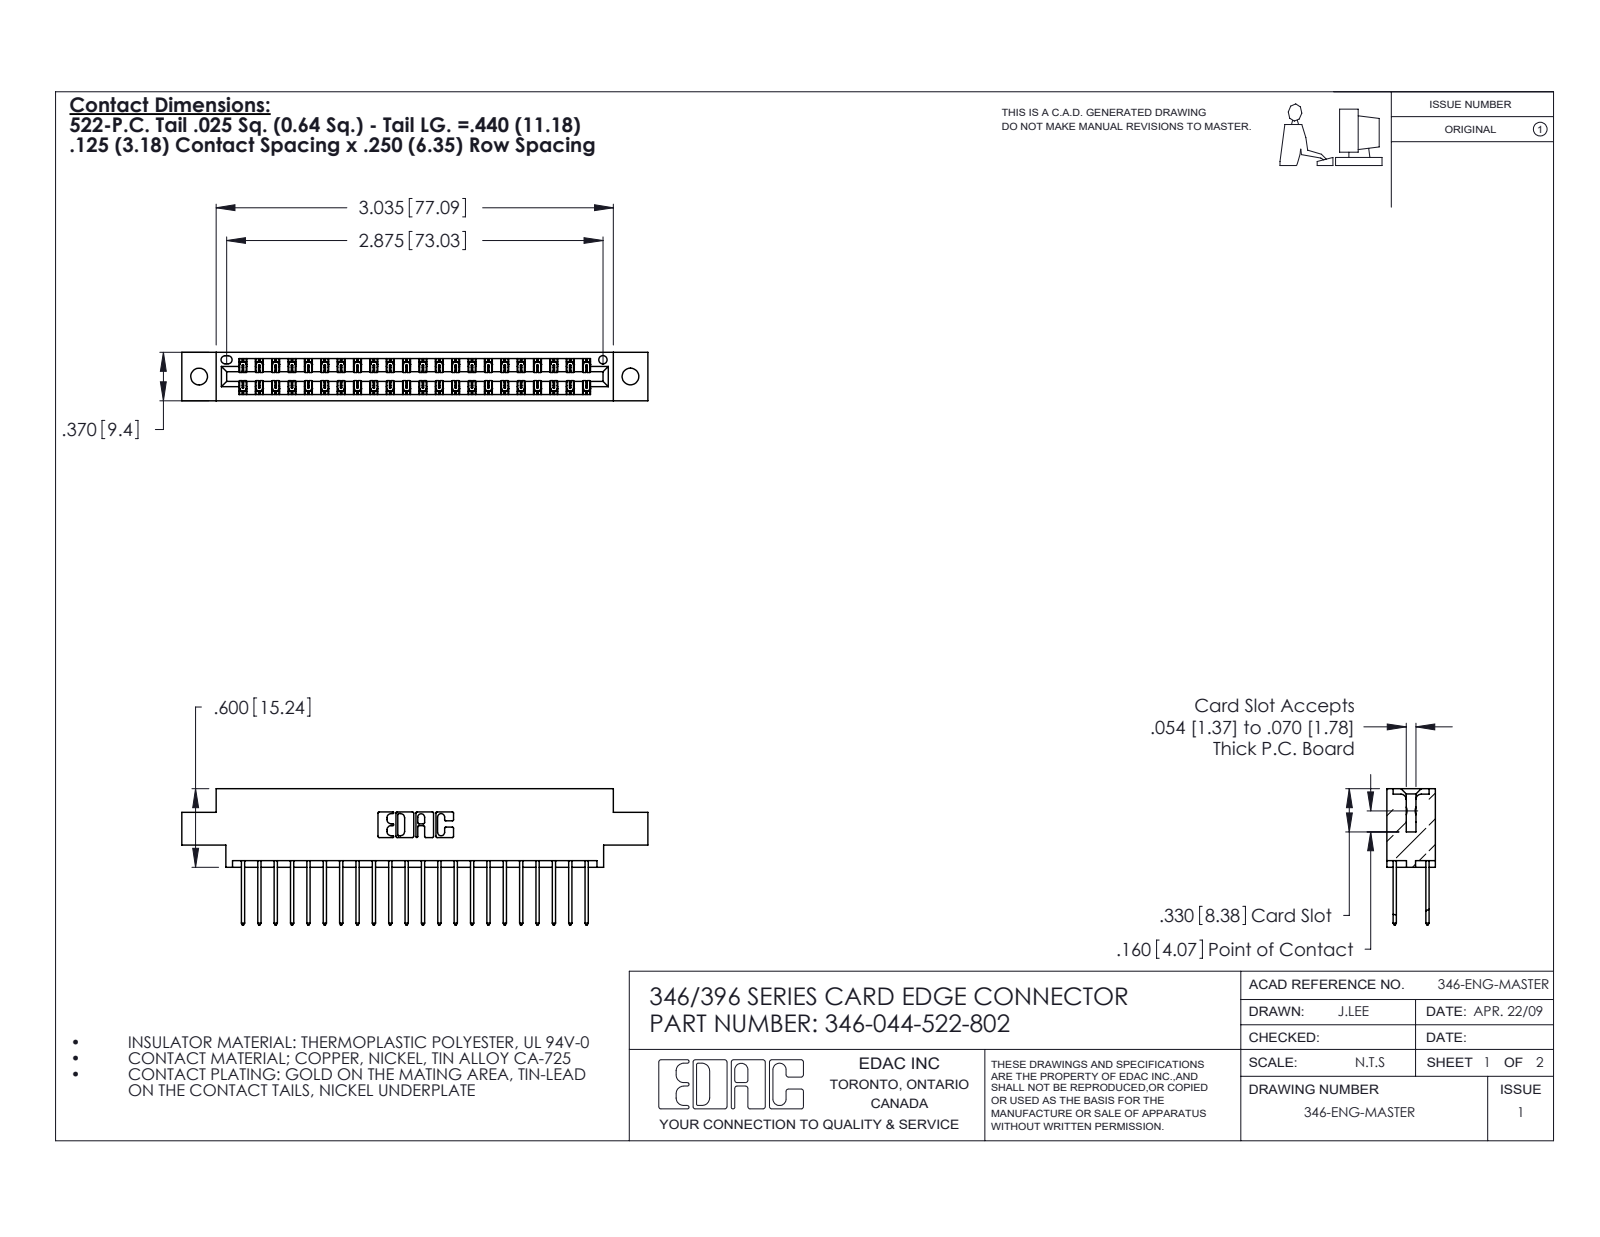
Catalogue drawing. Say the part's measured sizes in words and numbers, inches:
The part is named "346 Part_0.170 Offset - 0.128 Dia; 345-292-001_345-293-122; 346-044-522-802". Its 3-D file was written by "SolidWorks 2020 (CONFIG_CONTROL_DESIGN)". It is 45 solids with 2414 faces: 1620 planar, 794 cylindrical and 0 other. Overall it measures 3.56 by 1.04 by 0.37 inches. Its volume is 0.524 cubic inches and its surface area 18.47 square inches. Round holes: 2 of diameter 0.128, 1 of diameter 0.064. Partial cylindrical surfaces (rounded edges, fillets, slot ends): 66 of radius 0.006, 44 of radius 0.01, 22 of radius 0.01, 6 of radius 0.007, 6 of radius 0.031, 3 of radius 0.026, 2 of radius 0.014, 2 of radius 0.022. The main face-to-face distances are 0.048, 0.322, 0.25, 0.37, 0.072, 0.298, 0.025, 0.275, 0.148, 0.222. The hole center spacings are 0.246, 3.087, 3.295.
